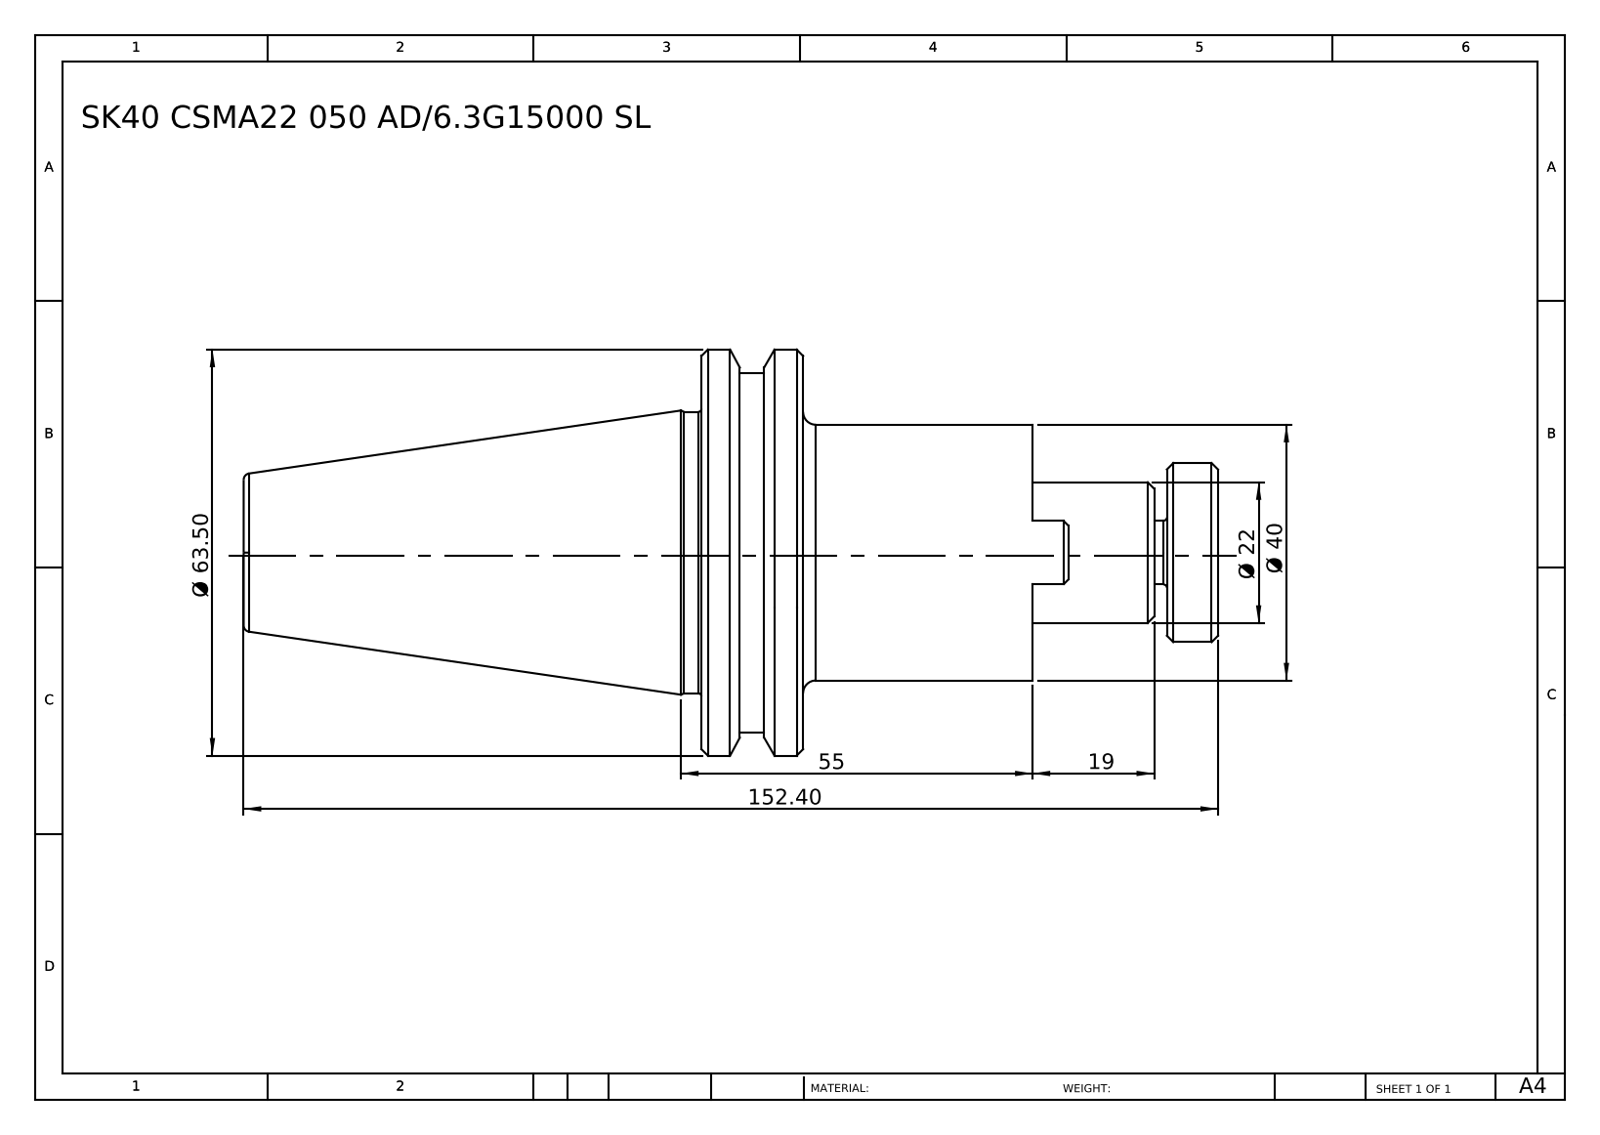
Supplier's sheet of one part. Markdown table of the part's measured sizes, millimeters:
| quantity | value |
| --- | --- |
| part name | SK 40 CSMA22 055 AD-6.3G15000 SL SP |
| STEP written by | SolidWorks 2014 (CONFIG_CONTROL_DESIGN) |
| units | millimeters |
| bodies | 1 solid, 72 faces (21 planar, 20 cylindrical, 31 other) |
| overall size | 152.4 × 63.5 × 63.5 |
| volume | 175 082 mm³ |
| surface area | 24 799 mm² |
| round bosses / shafts (diameter × count) | 63.5 × 1, 56.25 × 1, 44 × 1, 40 × 1, 28 × 1, 22 × 1, 10 × 1 |
| partial cylindrical surfaces (radius × count) | 3 × 1, 8.15 × 1, 13 × 1 |
| main face-to-face distances | 15.9, 35.9, 51.8, 29, 64.9, 80.8, 8, 21, 56.9, 72.8 |
